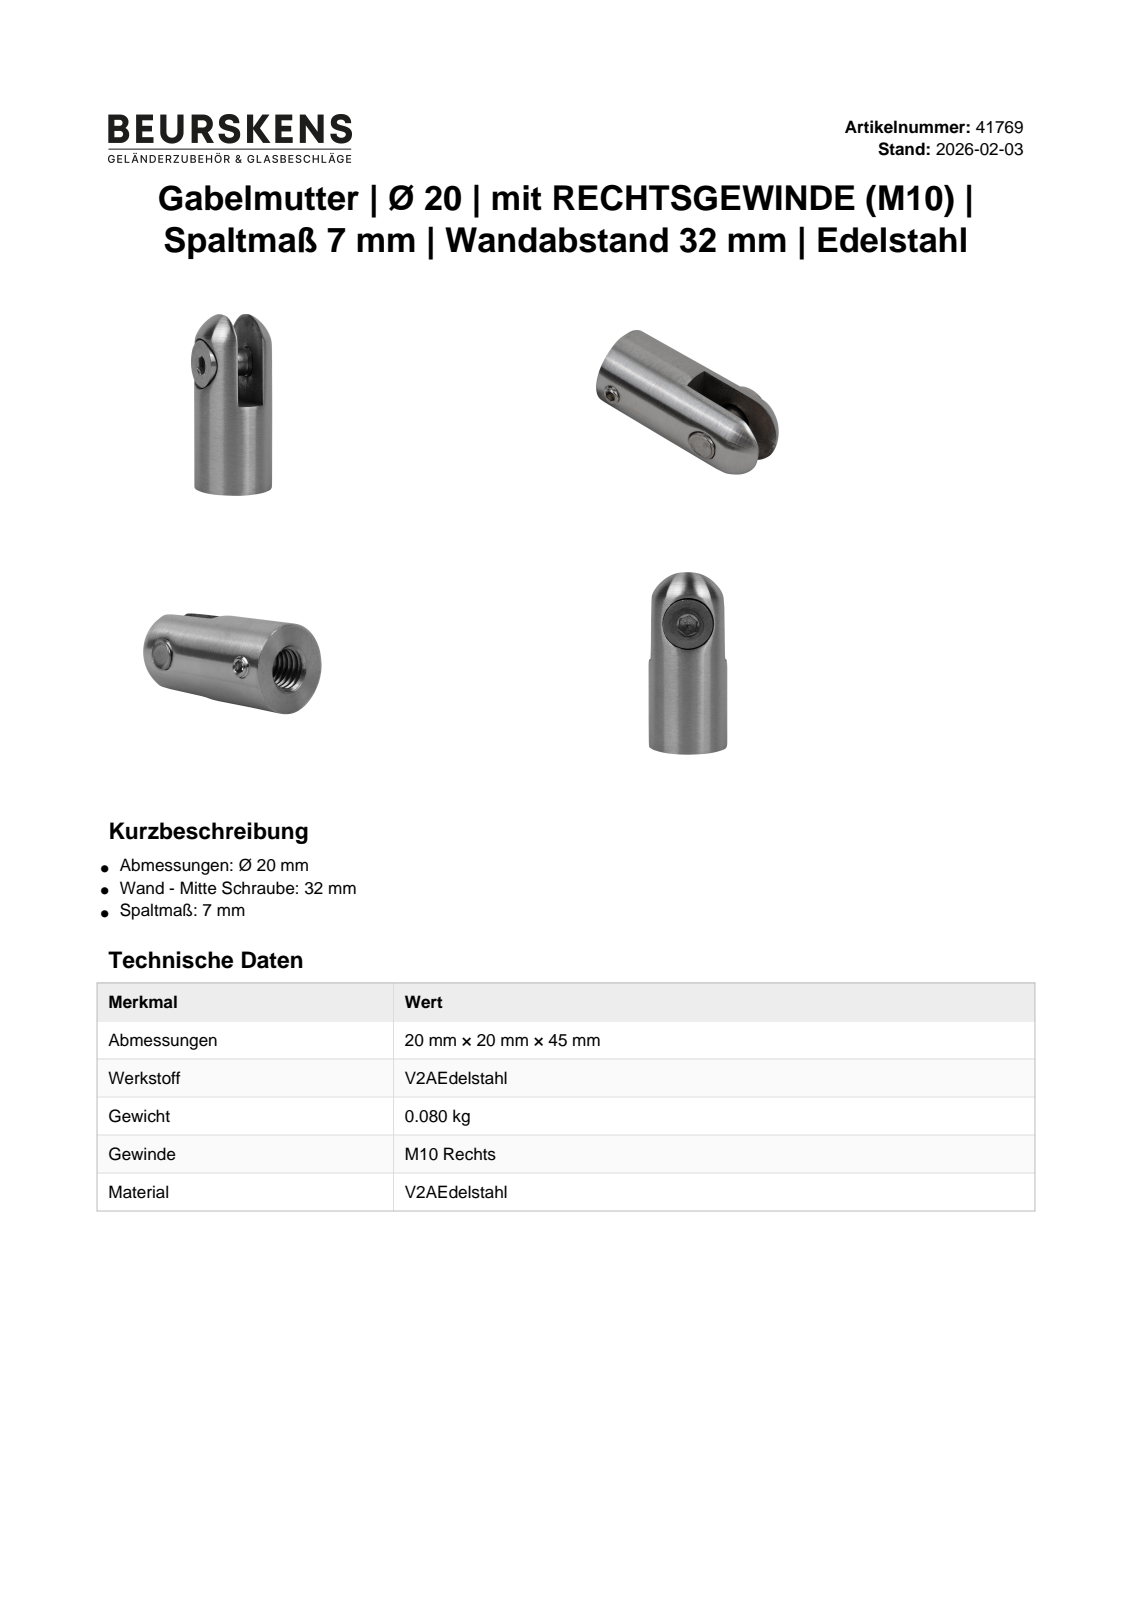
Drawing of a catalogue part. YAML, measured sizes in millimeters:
part_name: "41769"
step_written_by: "Autodesk Inventor 2022 (AUTOMOTIVE_DESIGN)"
units: millimeters
bodies: {solids: 1, faces: 17, planar: 7, cylindrical: 6, other: 4}
overall_size: [40.5, 20, 20]
volume: 7928
surface_area: 4044
round_holes:
  - {diameter: 5, count: 1}
  - {diameter: 8, count: 1}
  - {diameter: 8.5, count: 1}
  - {diameter: 12.5, count: 1}
round_bosses_or_shafts:
  - {diameter: 20, count: 1}
face_to_face_distances: [7, 22, 11, 4, 40.5, 18.5]
hole_center_spacings: [27]
